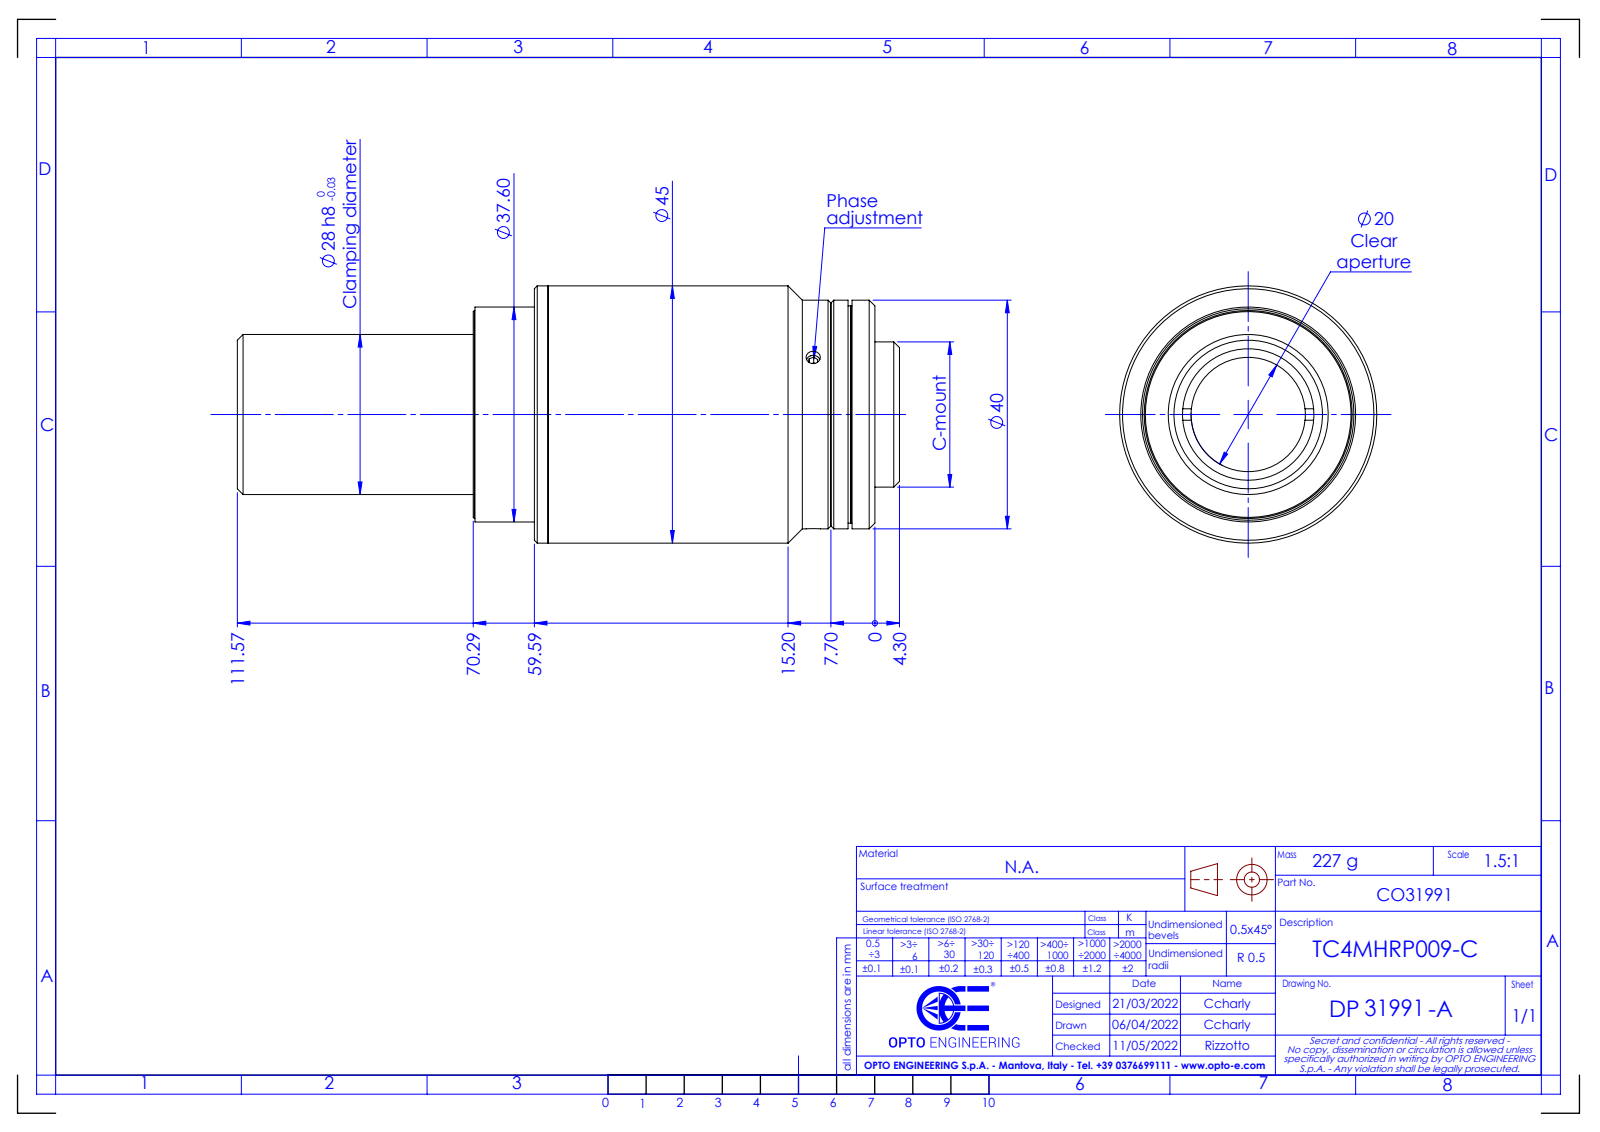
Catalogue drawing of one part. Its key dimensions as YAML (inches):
part_name: "DP31991-A_TC4MHRP009-C"
step_written_by: "SolidWorks 2021 (CONFIG_CONTROL_DESIGN)"
units: inches
bodies: {solids: 0, faces: 79, planar: 29, cylindrical: 30, other: 20}
overall_size: [4.562, 1.772, 1.772]
round_holes:
  - {diameter: 0.098, count: 3}
  - {diameter: 0.787, count: 1}
  - {diameter: 0.886, count: 1}
  - {diameter: 0.906, count: 1}
round_bosses_or_shafts:
  - {diameter: 1.772, count: 1}
  - {diameter: 1.575, count: 1}
  - {diameter: 1.48, count: 1}
  - {diameter: 1.433, count: 1}
  - {diameter: 1.102, count: 1}
  - {diameter: 1, count: 1}
face_to_face_distances: [0.028, 0.185, 0.157, 0.118, 0.146, 0.303, 2.464, 2.582, 2.61, 2.767]
